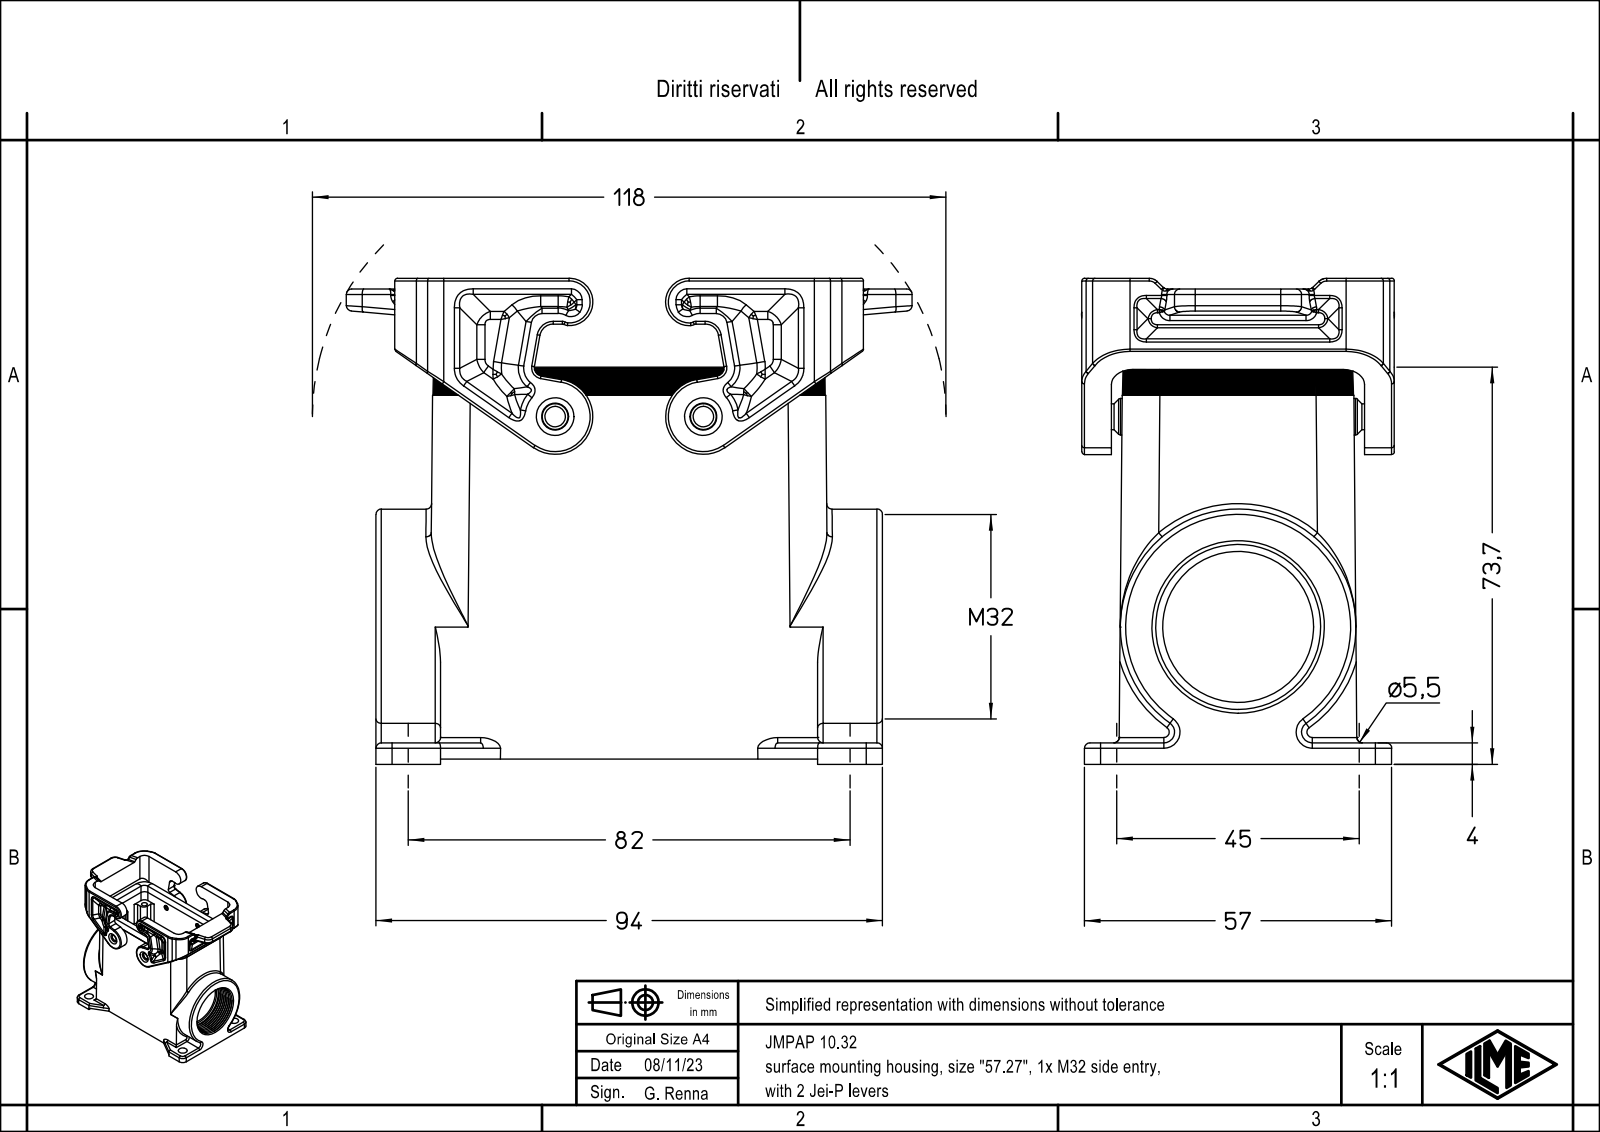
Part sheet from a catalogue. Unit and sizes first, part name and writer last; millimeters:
Units: millimetres
Overall size (bounding box): 105 × 90.2 × 58.08
Round holes (diameter × count): ⌀3 ×4, ⌀3.5 ×4, ⌀5.5 ×4, ⌀4.8 ×2, ⌀28 ×1, ⌀30.6 ×1
Round bosses / shafts (diameter × count): ⌀6.8 ×2, ⌀43.75 ×1
Partial cylindrical surfaces — rounded edges, fillets, slot ends (radius × count): R0.5 ×50, R1 ×44, R3 ×38, R2 ×26, R1.5 ×12, R4 ×12, R6 ×12, R7 ×10
Main face-to-face distances: 3, 8.5, 1, 4, 47, 85.5, 5.5, 2, 52.5, 94
Hole centre spacings: 15.4, 38.11, 70.08, 78.27, 27, 45, 57, 63.07
Volume: 128 939 mm³ · Surface area: 56 323 mm²
Bodies: 1 solid, 868 faces (173 planar, 314 cylindrical, 381 other)
Part name (STEP PRODUCT): JMPAP 10.32
STEP written by: Creo Elements/Direct Modeling 20.1B 02-Apr-2019 (C) Parametric Technology GmbH (AUTOMOTIVE_DESIGN)
